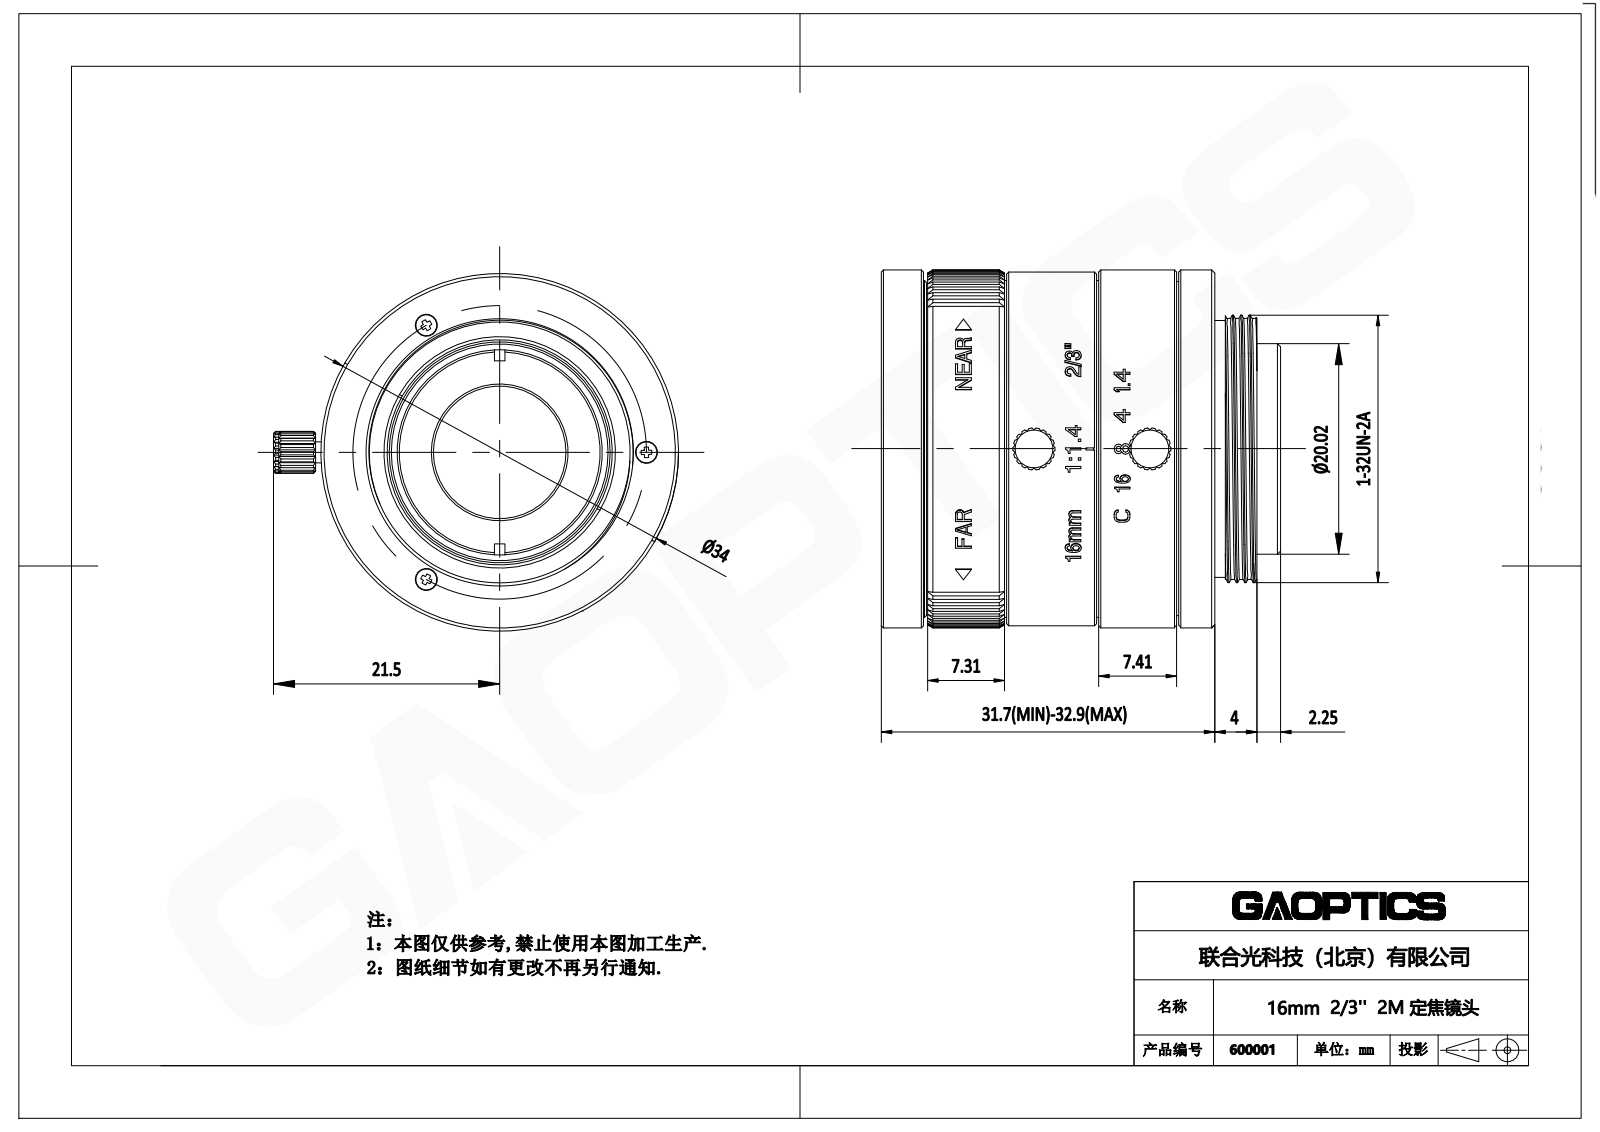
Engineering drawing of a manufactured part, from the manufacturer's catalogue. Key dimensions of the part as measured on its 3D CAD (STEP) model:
Part name (STEP PRODUCT): 600001
STEP written by: SolidWorks 2020 (CONFIG_CONTROL_DESIGN)
Units: millimetres
Bodies: 9 solids, 1351 faces (547 planar, 309 cylindrical, 495 other)
Overall size (bounding box): 38.25 × 37.92 × 34
Volume: 28 202 mm³ · Surface area: 12 824 mm²
Round holes (diameter × count): ⌀1.4 ×2, ⌀1.2 ×1, ⌀2 ×1, ⌀2.6 ×1, ⌀14 ×1, ⌀15.4 ×1, ⌀17.85 ×1, ⌀18.4 ×1, ⌀20 ×1, ⌀20.6 ×1, ⌀21 ×1, ⌀21.2 ×1
Round bosses / shafts (diameter × count): ⌀2 ×5, ⌀1.4 ×2, ⌀34 ×1, ⌀33.6 ×1, ⌀32 ×1, ⌀31.8 ×1, ⌀31.25 ×1, ⌀30.4 ×1
Partial cylindrical surfaces — rounded edges, fillets, slot ends (radius × count): R0.5 ×7, R2 ×2, R16.88 ×1, R16.89 ×1, R17.08 ×1, R17.09 ×1
Main face-to-face distances: 26, 1.33, 4, 31.51, 5.72, 30.76, 3.57, 29.57, 31.9, 3.43
